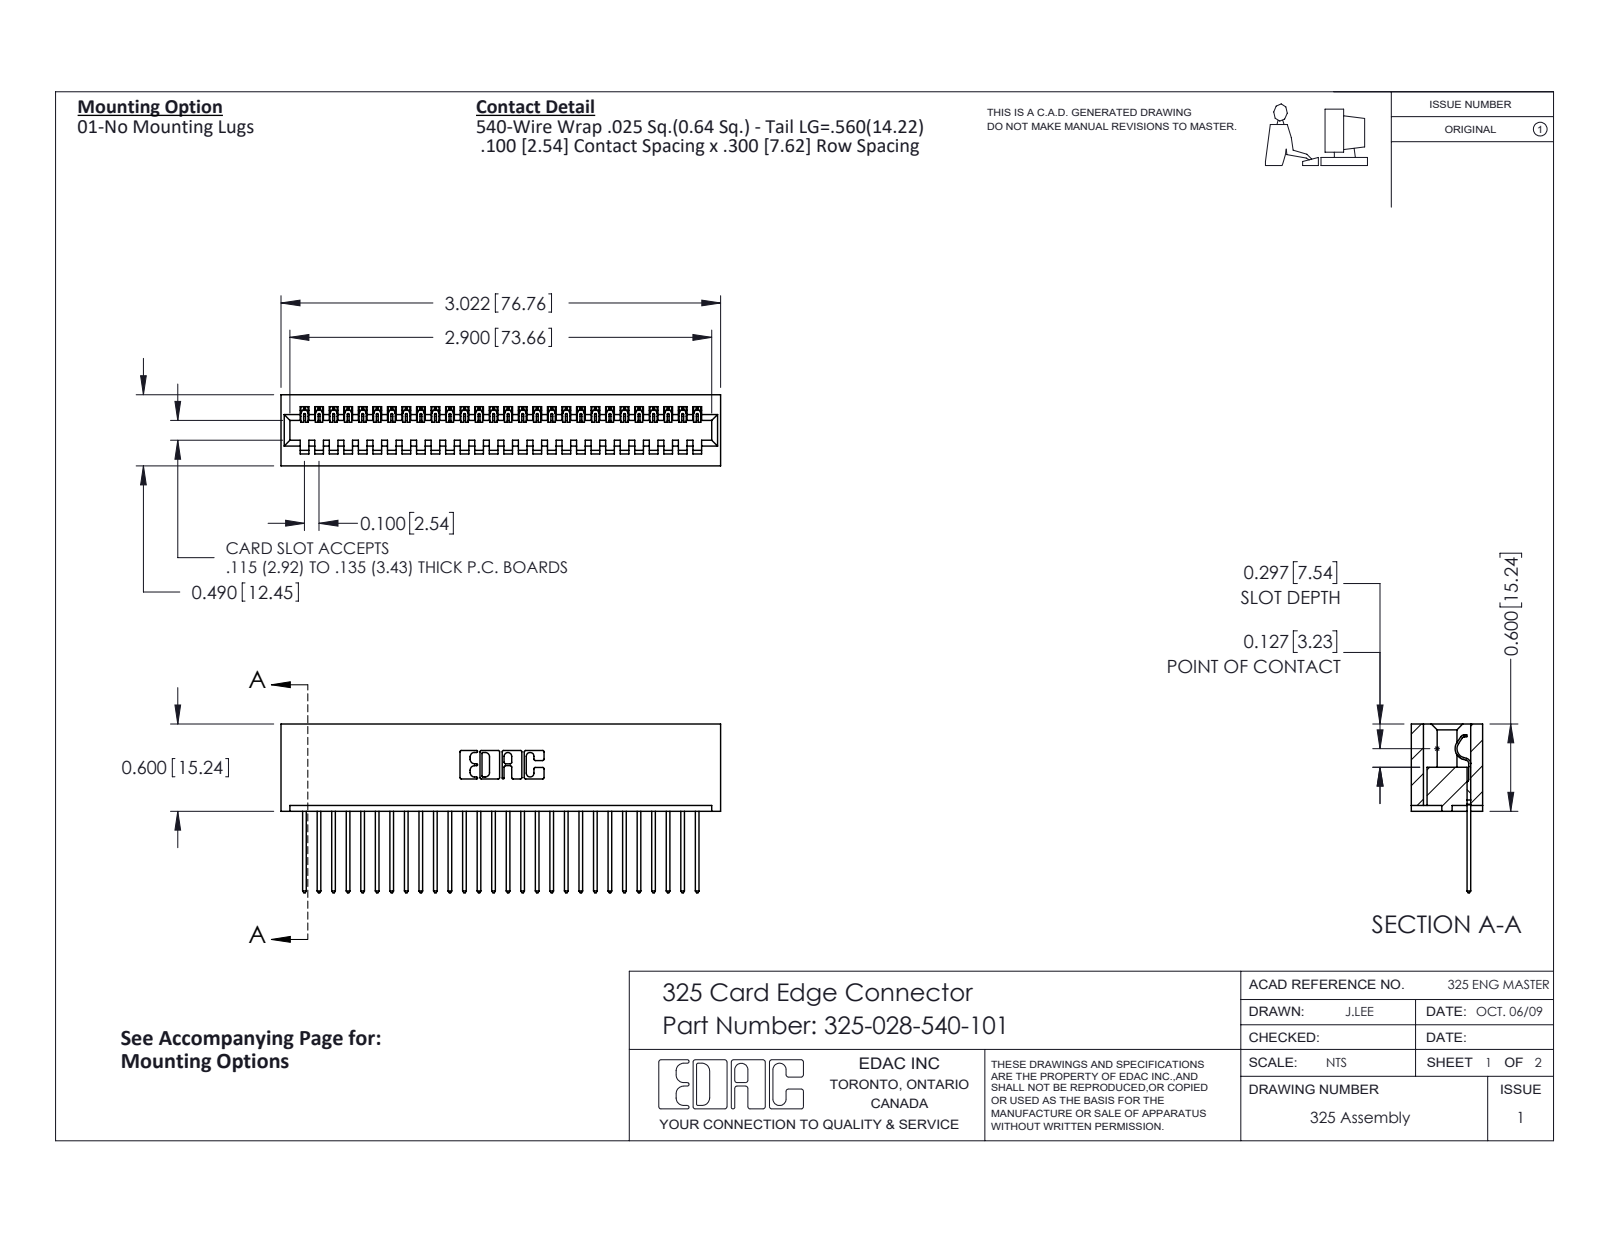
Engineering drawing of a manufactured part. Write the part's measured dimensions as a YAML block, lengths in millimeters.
part_name: "325-028-540-101; 325-292-001_325-293-140; 325 Part_Lugless"
step_written_by: "SolidWorks 2016 (CONFIG_CONTROL_DESIGN)"
units: millimeters
bodies: {solids: 29, faces: 1730, planar: 1242, cylindrical: 488, other: 0}
overall_size: [76.8, 29.5, 12.4]
volume: 10200
surface_area: 11720
partial_cylinders:
  - {radius: 0.2, count: 56}
  - {radius: 0.3, count: 56}
  - {radius: 0.3, count: 22}
  - {radius: 0.2, count: 6}
  - {radius: 0.8, count: 6}
  - {radius: 0.7, count: 3}
  - {radius: 0.4, count: 1}
  - {radius: 0.6, count: 1}
face_to_face_distances: [2.1, 10.3, 7.6, 12.4, 2.7, 9.7, 0.6, 8.3, 14.2, 6.7]
